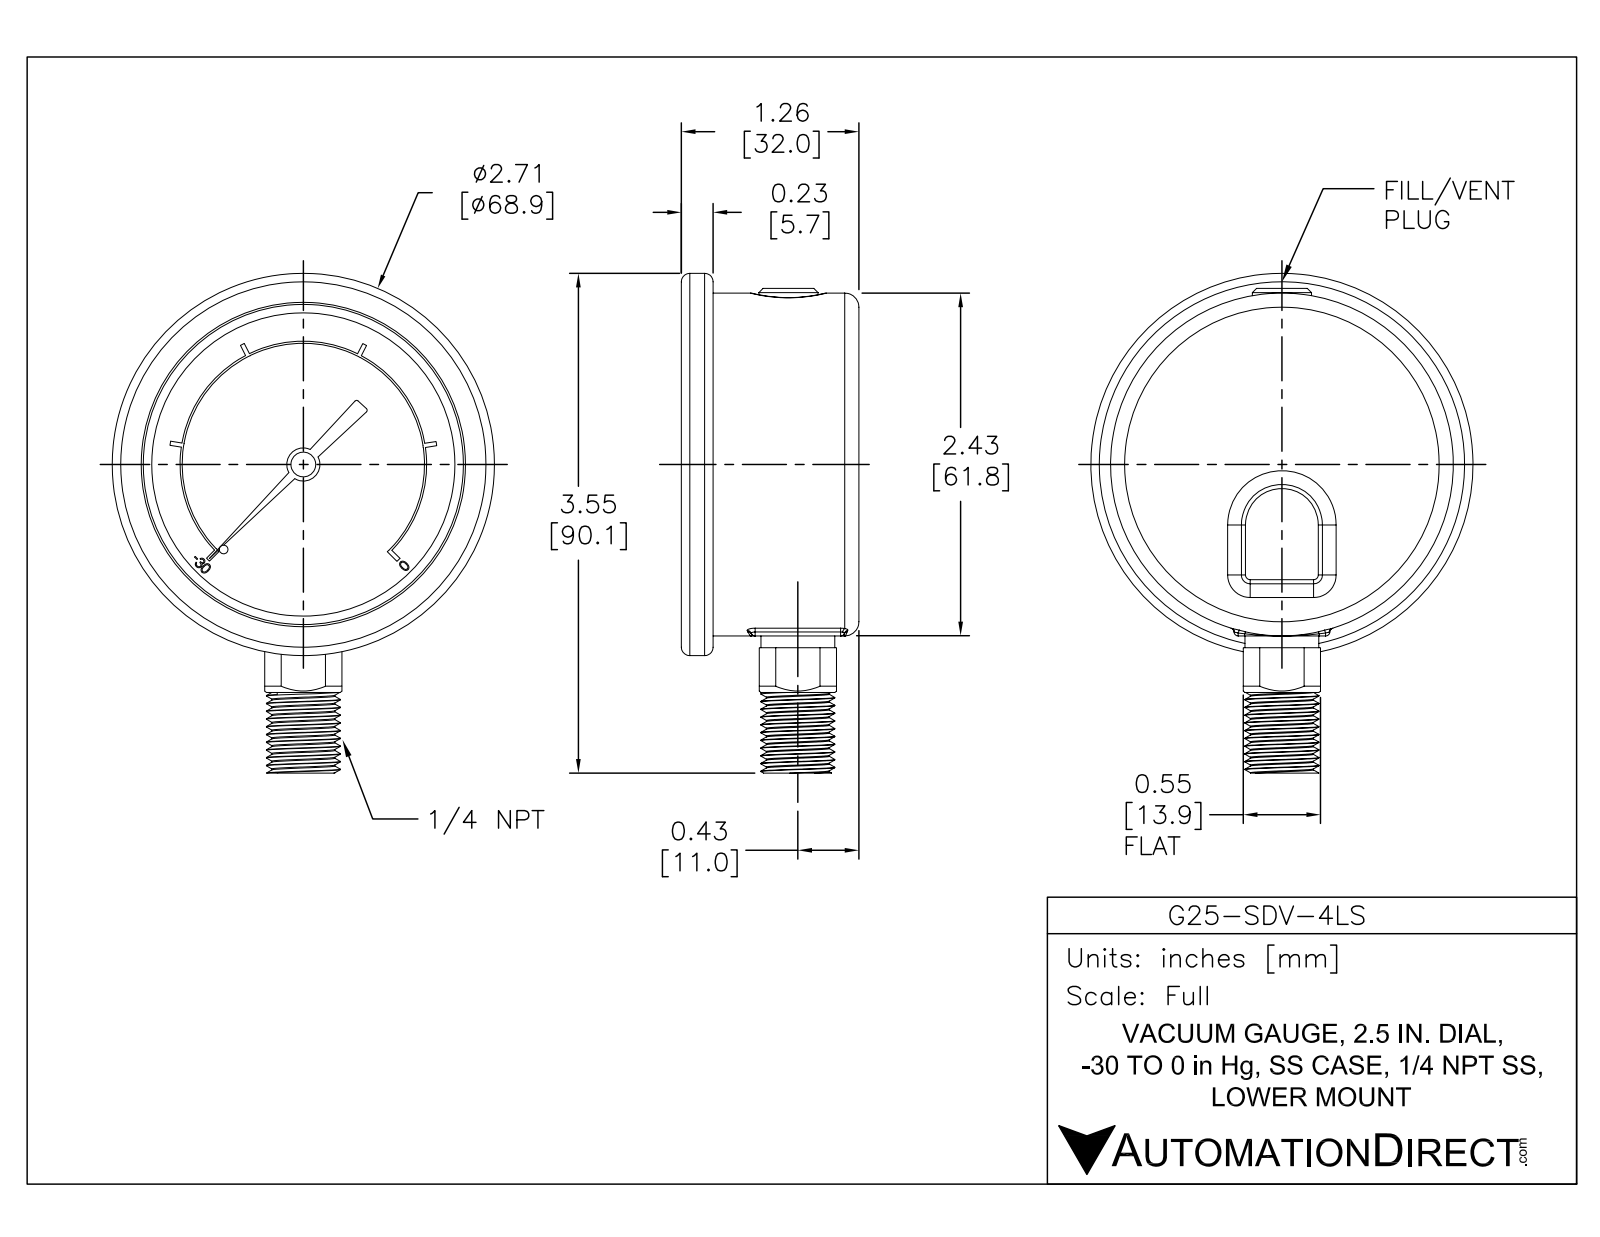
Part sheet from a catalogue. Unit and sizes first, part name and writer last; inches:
Units: inches
Overall size (bounding box): 3.546 × 2.713 × 1.26
Round holes (diameter × count): ⌀0.027 ×1, ⌀0.071 ×1, ⌀0.119 ×1, ⌀2.272 ×1
Round bosses / shafts (diameter × count): ⌀2.713 ×1, ⌀2.433 ×1, ⌀0.524 ×1, ⌀0.42 ×1, ⌀0.235 ×1, ⌀0.176 ×1, ⌀0.14 ×1, ⌀0.041 ×1
Partial cylindrical surfaces — rounded edges, fillets, slot ends (radius × count): R0.03 ×9, R0.1 ×3, R0.015 ×2, R0.316 ×1, R0.86 ×1, R0.875 ×1
Main face-to-face distances: 1.01, 1.26, 0.25, 1.035, 0.025, 0.225, 0.1, 0.91, 0.935, 1.16
Hole centre spacings: 0.067
Volume: 5.273 in³ · Surface area: 24.68 in²
Bodies: 1 solid, 347 faces (195 planar, 85 cylindrical, 67 other)
Part name (STEP PRODUCT): G25-SDV-4LS
STEP written by: SolidWorks 2021 (AUTOMOTIVE_DESIGN)
